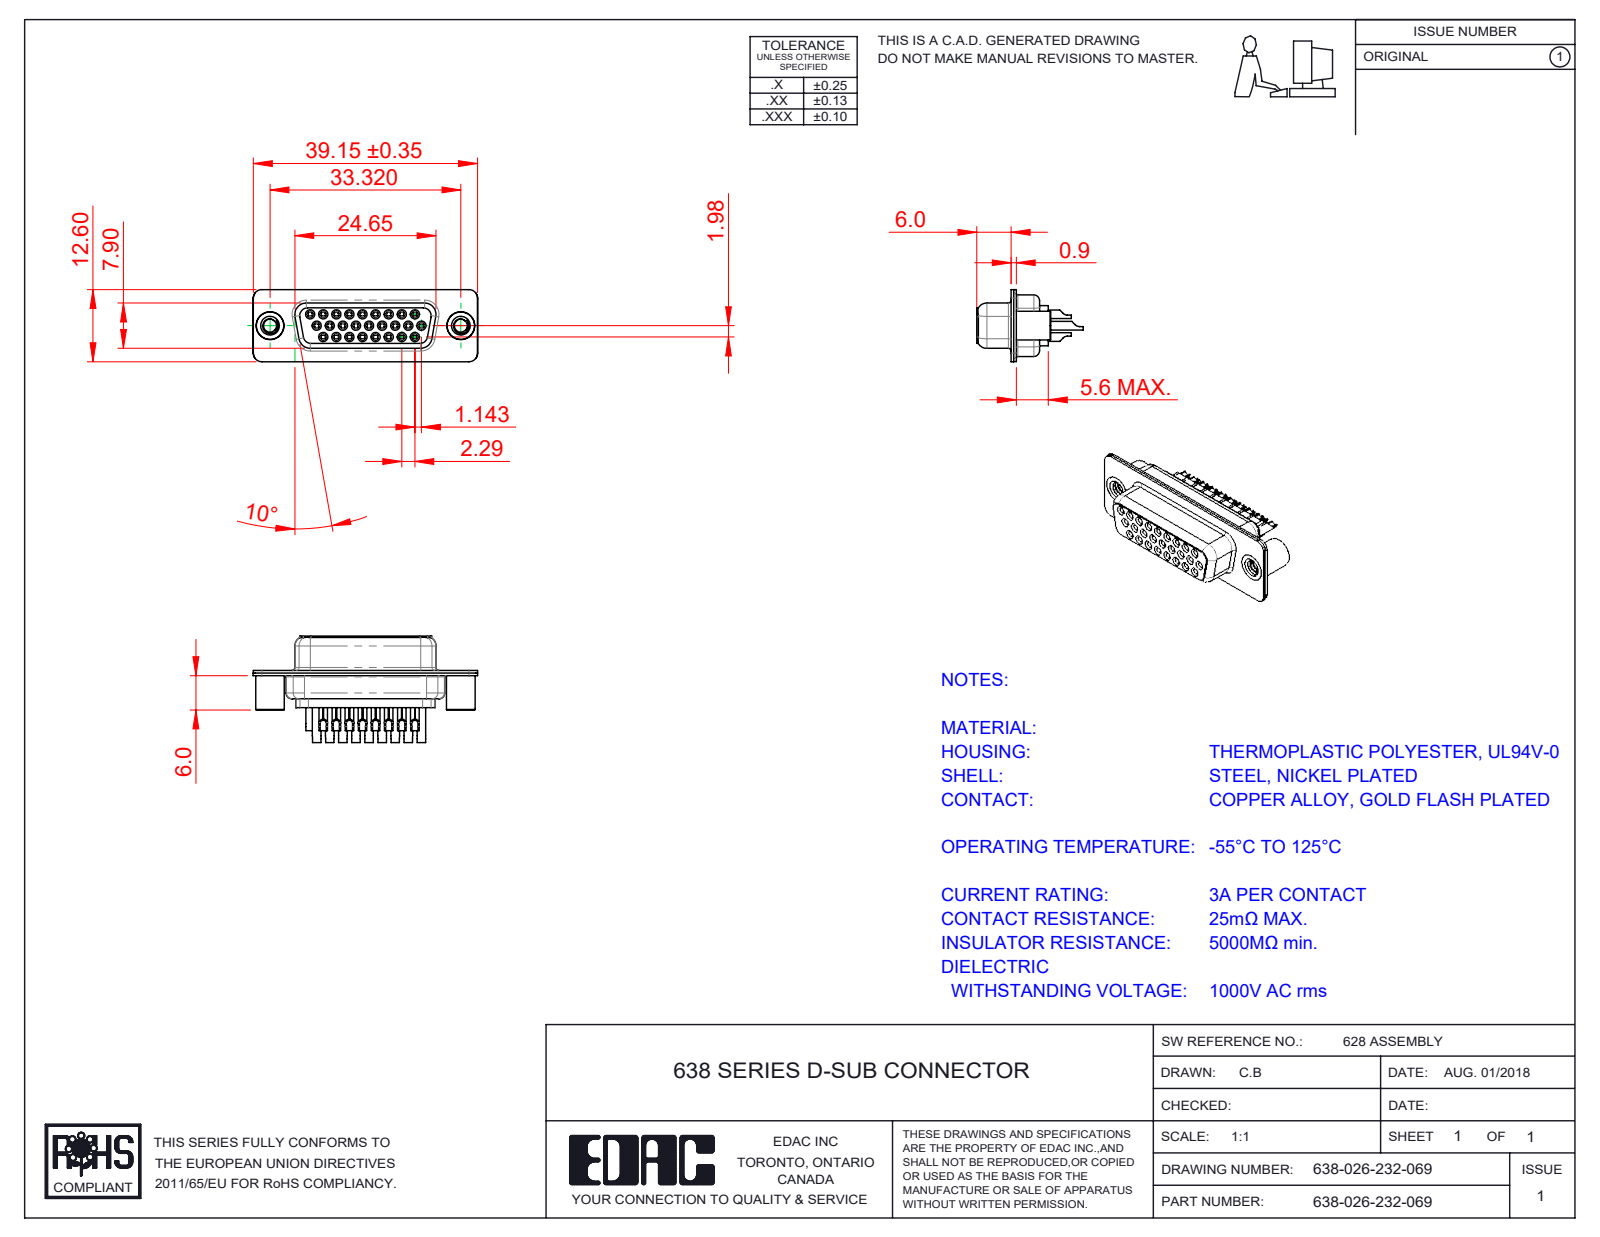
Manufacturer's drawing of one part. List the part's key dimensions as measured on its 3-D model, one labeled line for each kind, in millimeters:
Part name (STEP PRODUCT): 638 Contact Row 1_32; 638 Contact Row 3_32; 638 Contact Row 2_32; 638 Housing_26 Contacts (+4 more)
STEP written by: SolidWorks 2020 (CONFIG_CONTROL_DESIGN)
Units: millimetres
Bodies: 31 solids, 2615 faces (613 planar, 807 cylindrical, 1195 other)
Overall size (bounding box): 39.19 × 18.6 × 12.6
Volume: 2 357 mm³ · Surface area: 8 957 mm²
Round holes (diameter × count): ⌀0.8 ×26, ⌀1 ×26, ⌀1.1 ×26, ⌀1.6 ×26, ⌀1.7 ×26, ⌀1.8 ×26, ⌀2.26 ×2, ⌀4 ×2, ⌀4.05 ×2, ⌀4.85 ×2
Round bosses / shafts (diameter × count): ⌀2 ×26, ⌀1.5 ×26, ⌀1.2 ×26, ⌀5 ×2, ⌀4.95 ×2, ⌀4.8 ×2
Partial cylindrical surfaces — rounded edges, fillets, slot ends (radius × count): R1.5 ×20, R0.28 ×18, R2 ×12, R1.55 ×8, R1 ×7, R1.35 ×5, R0.25 ×4, R0.5 ×4
Main face-to-face distances: 0.45, 0.4, 1.43, 8.88, 6.6, 0.9, 1.4, 2.28, 0.85, 7.05
Hole centre spacings: 3.96, 2.28, 4.57, 6.05, 2.29, 8.24, 6.86, 10.48
